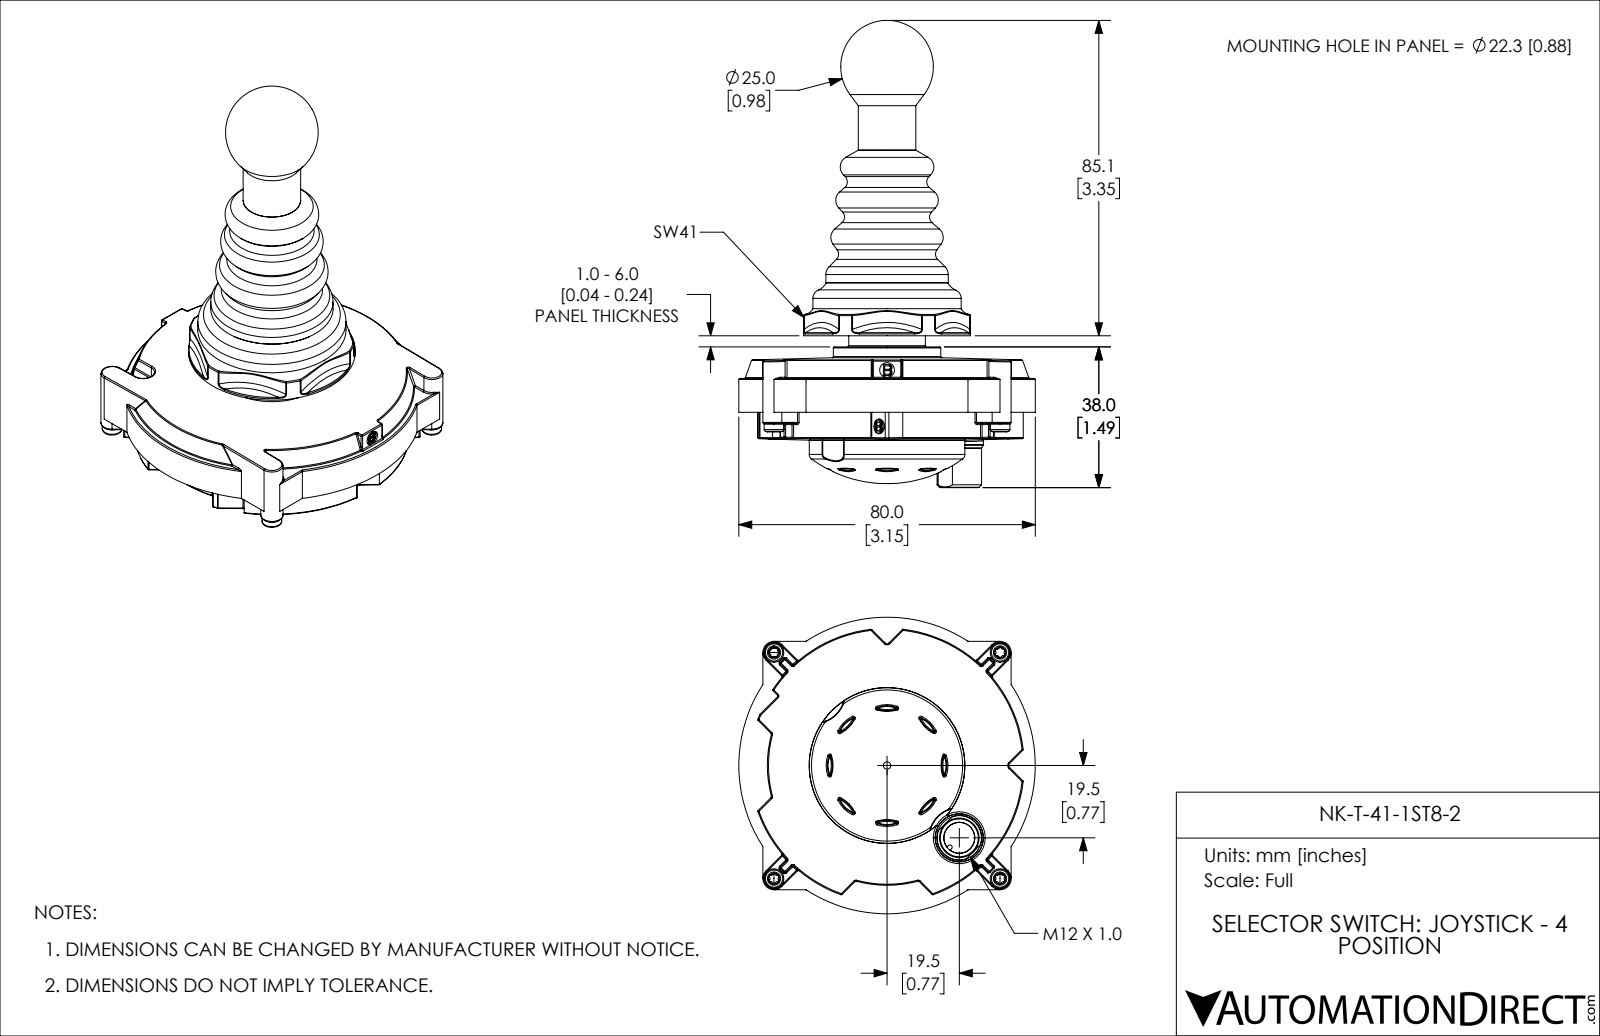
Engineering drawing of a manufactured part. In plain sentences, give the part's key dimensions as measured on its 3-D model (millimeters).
The part is named "NK-T-41-1ST8-2". Its 3-D file was written by "SolidWorks 2019 (CONFIG_CONTROL_DESIGN)". It is 4 solids with 1358 faces: 374 planar, 341 cylindrical and 643 other. Overall it measures 126.01 by 80 by 80 millimeters. Its volume is 165 568 cubic millimeters and its surface area 32 398 square millimeters. Round holes: 5 of diameter 4, 4 of diameter 2.93, 1 of diameter 8.3, 1 of diameter 8.4, 1 of diameter 31.2, 1 of diameter 37.1, 1 of diameter 40.1. Round bosses or shafts: 4 of diameter 5.3, 1 of diameter 45, 1 of diameter 42, 1 of diameter 40, 1 of diameter 33.1, 1 of diameter 33, 1 of diameter 29, 1 of diameter 25. Partial cylindrical surfaces (rounded edges, fillets, slot ends): 115 of radius 0.3, 44 of radius 0.19, 12 of radius 0.5, 8 of radius 2.58, 8 of radius 9, 7 of radius 0.6, 5 of radius 3, 2 of radius 0.69. The main face-to-face distances are 34.95, 14.1, 20.85, 67, 70.71, 49.86, 35.76, 25.8, 9.15, 11.7. The hole center spacings are 61, 43.13, 4.5, 51.2, 56.5, 86.27, 15.56, 27.58.
